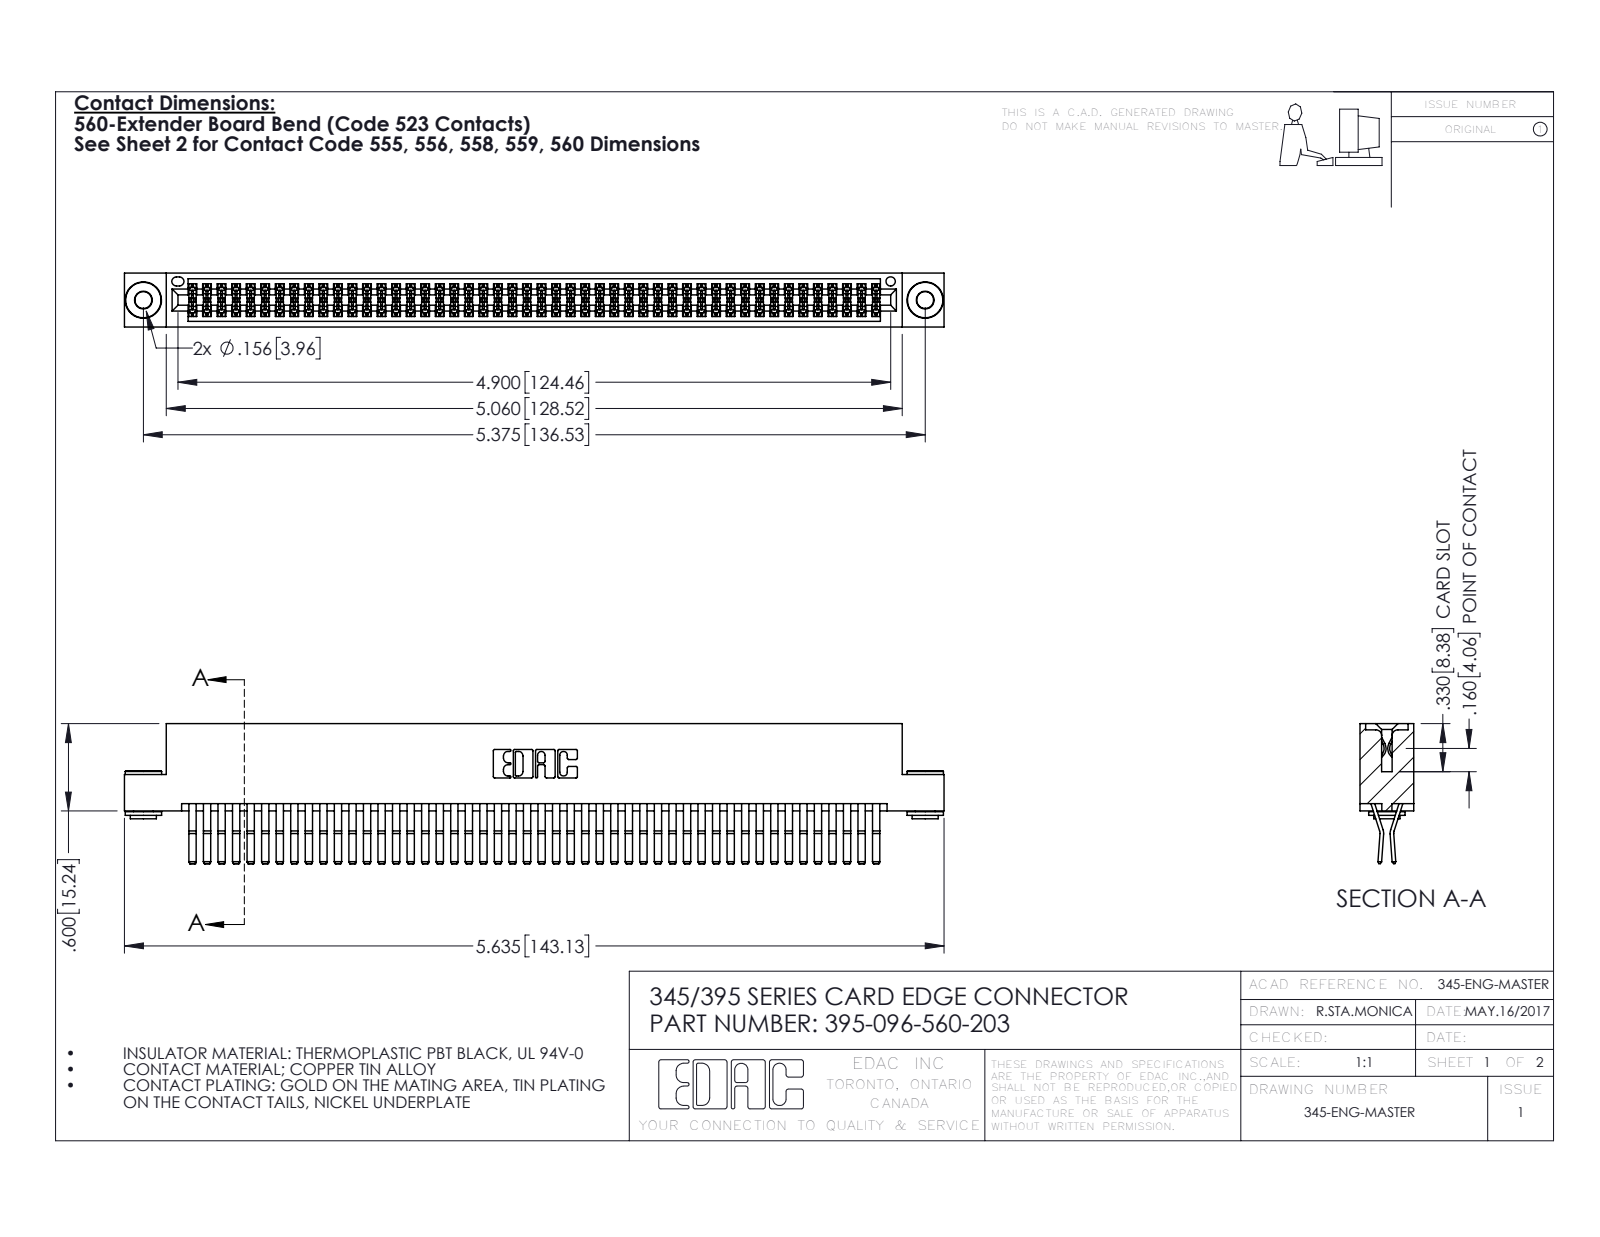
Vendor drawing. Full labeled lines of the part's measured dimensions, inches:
Part name (STEP PRODUCT): 395-096-560-203; 345-250-002_345-250-002-102; 345-292-001_560 Tail; 345 Part_Flush Mounting Lugs - 0.156 Dia-TH
STEP written by: SolidWorks 2016 (CONFIG_CONTROL_DESIGN)
Units: inches
Bodies: 99 solids, 5156 faces (3258 planar, 1890 cylindrical, 8 other)
Overall size (bounding box): 5.635 × 0.962 × 0.37
Volume: 0.891 in³ · Surface area: 36.48 in²
Round holes (diameter × count): ⌀0.116 ×2, ⌀0.156 ×2, ⌀0.064 ×1
Round bosses / shafts (diameter × count): ⌀0.25 ×2, ⌀0.18 ×2, ⌀0.136 ×2
Partial cylindrical surfaces — rounded edges, fillets, slot ends (radius × count): R0.006 ×144, R0.01 ×22, R0.007 ×6, R0.031 ×6, R0.026 ×3, R0.01 ×2, R0.014 ×2, R0.019 ×2
Main face-to-face distances: 0.025, 0.072, 0.298, 0.37, 0.2, 0.098, 0.272, 0.225, 0.175, 0.149
Hole centre spacings: 0.27, 5.139, 5.375
